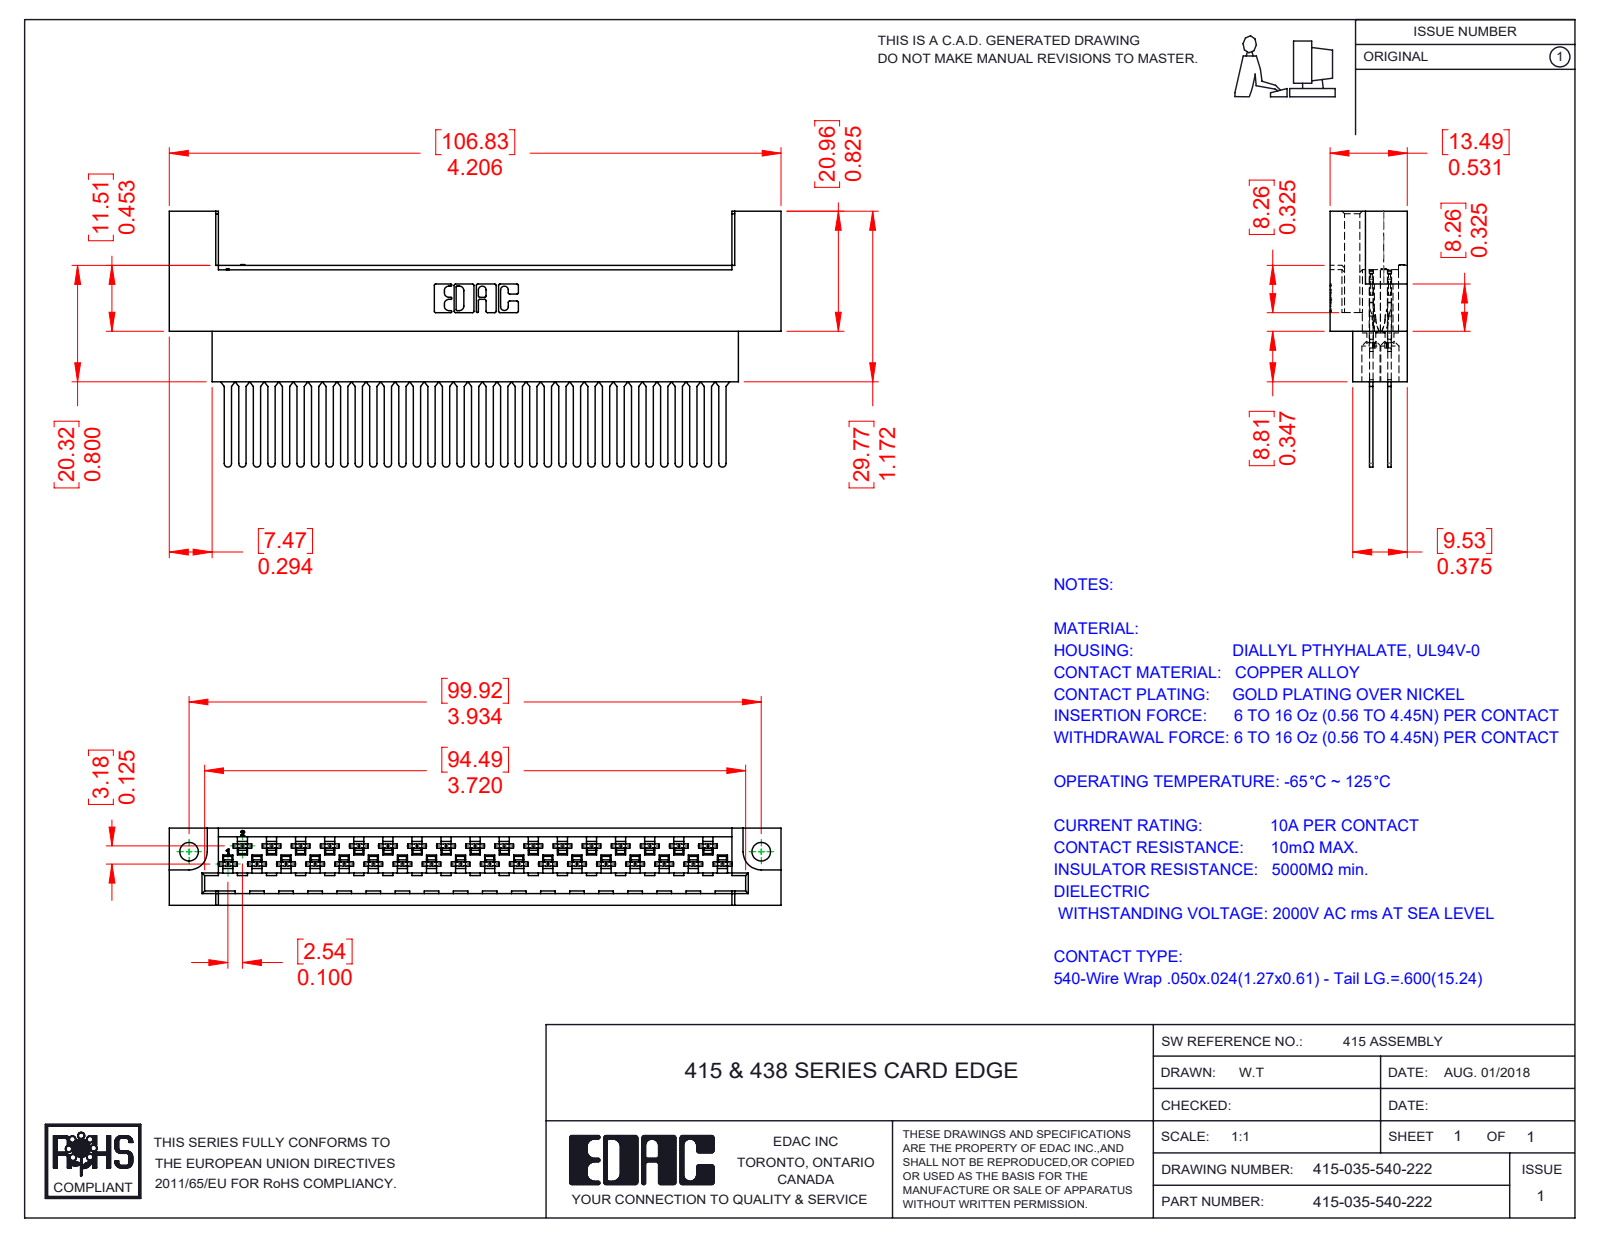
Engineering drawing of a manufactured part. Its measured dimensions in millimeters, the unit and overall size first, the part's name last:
Units: millimetres
Overall size (bounding box): 106.83 × 44.66 × 13.49
Round holes (diameter × count): ⌀1.27 ×35, ⌀3.3 ×35, ⌀3.25 ×2
Partial cylindrical surfaces — rounded edges, fillets, slot ends (radius × count): R0.3 ×140, R0.56 ×140, R0.18 ×70, R0.2 ×70, R0.41 ×70, R2.03 ×70, R0.64 ×35, R0.25 ×22
Main face-to-face distances: 3.18, 0.61, 7.49, 13.49, 1.27, 1.88, 6.61, 6.88, 6, 2.82
Hole centre spacings: 5.08, 10.16, 15.24, 20.32, 25.4, 30.48, 35.56, 2.54
Volume: 18 676 mm³ · Surface area: 24 474 mm²
Bodies: 36 solids, 3590 faces (2297 planar, 956 cylindrical, 337 other)
Part name (STEP PRODUCT): 415-035-540-222; 516-290-001_540; 415-210-001_415-210-035-222
STEP written by: SolidWorks 2016 (CONFIG_CONTROL_DESIGN)
